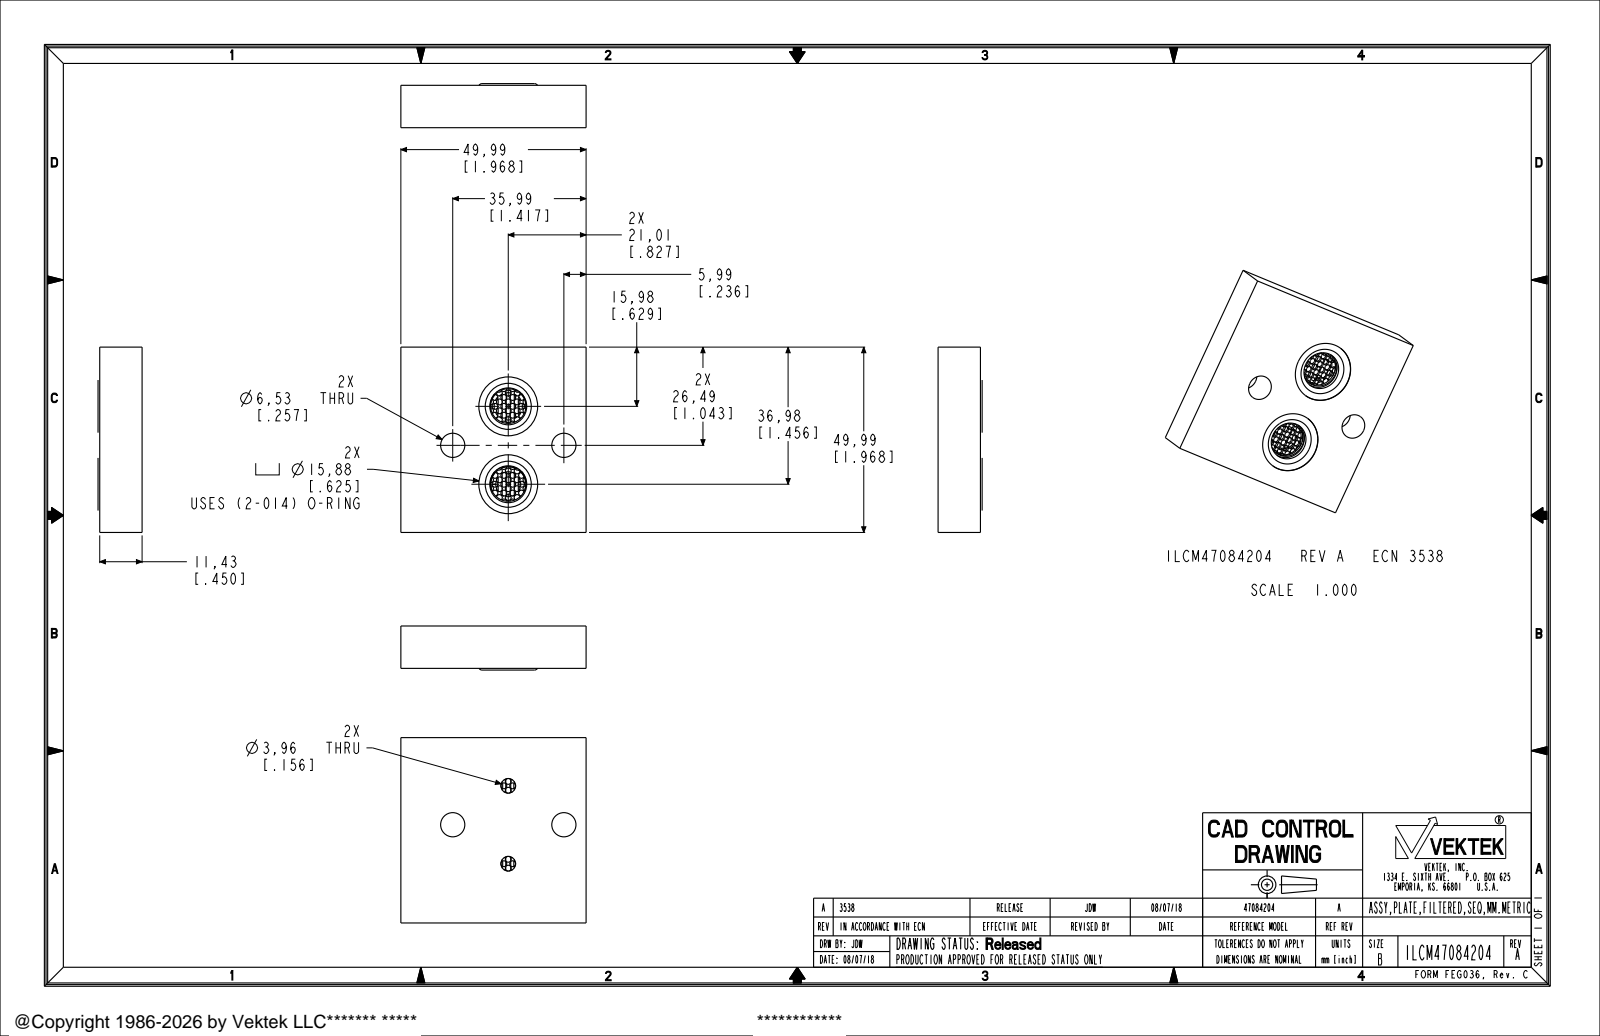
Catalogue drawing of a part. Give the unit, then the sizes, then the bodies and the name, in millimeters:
Units: millimetres
Overall size (bounding box): 50 × 50 × 11.9
Round holes (diameter × count): ⌀1.6 ×32, ⌀4 ×2, ⌀6.5 ×2, ⌀7.4 ×2, ⌀10 ×2, ⌀10.4 ×2, ⌀15.9 ×2, ⌀6.7 ×1
Round bosses / shafts (diameter × count): ⌀9.5 ×2, ⌀9.4 ×1, ⌀7.6 ×1
Partial cylindrical surfaces — rounded edges, fillets, slot ends (radius × count): R0.8 ×32, R0.5 ×7, R0.3 ×4, R0.4 ×4, R0.4 ×4, R0.6 ×4, R0.7 ×3, R4.8 ×2
Main face-to-face distances: 11.4, 50, 10.1, 1.3, 3.3, 2.5, 1.7, 2.5, 5, 0.8
Hole centre spacings: 2.4, 5.3, 3.4, 3.8, 22.2, 1.7, 1.7, 3.8
Volume: 26 330 mm³ · Surface area: 10 050 mm²
Bodies: 2 solids, 540 faces (130 planar, 402 cylindrical, 8 other)
Part name (STEP PRODUCT): ILCM47084204
STEP written by: PRO/ENGINEER BY PARAMETRIC TECHNOLOGY CORPORATION, 2013320 (AUTOMOTIVE_DESIGN)
